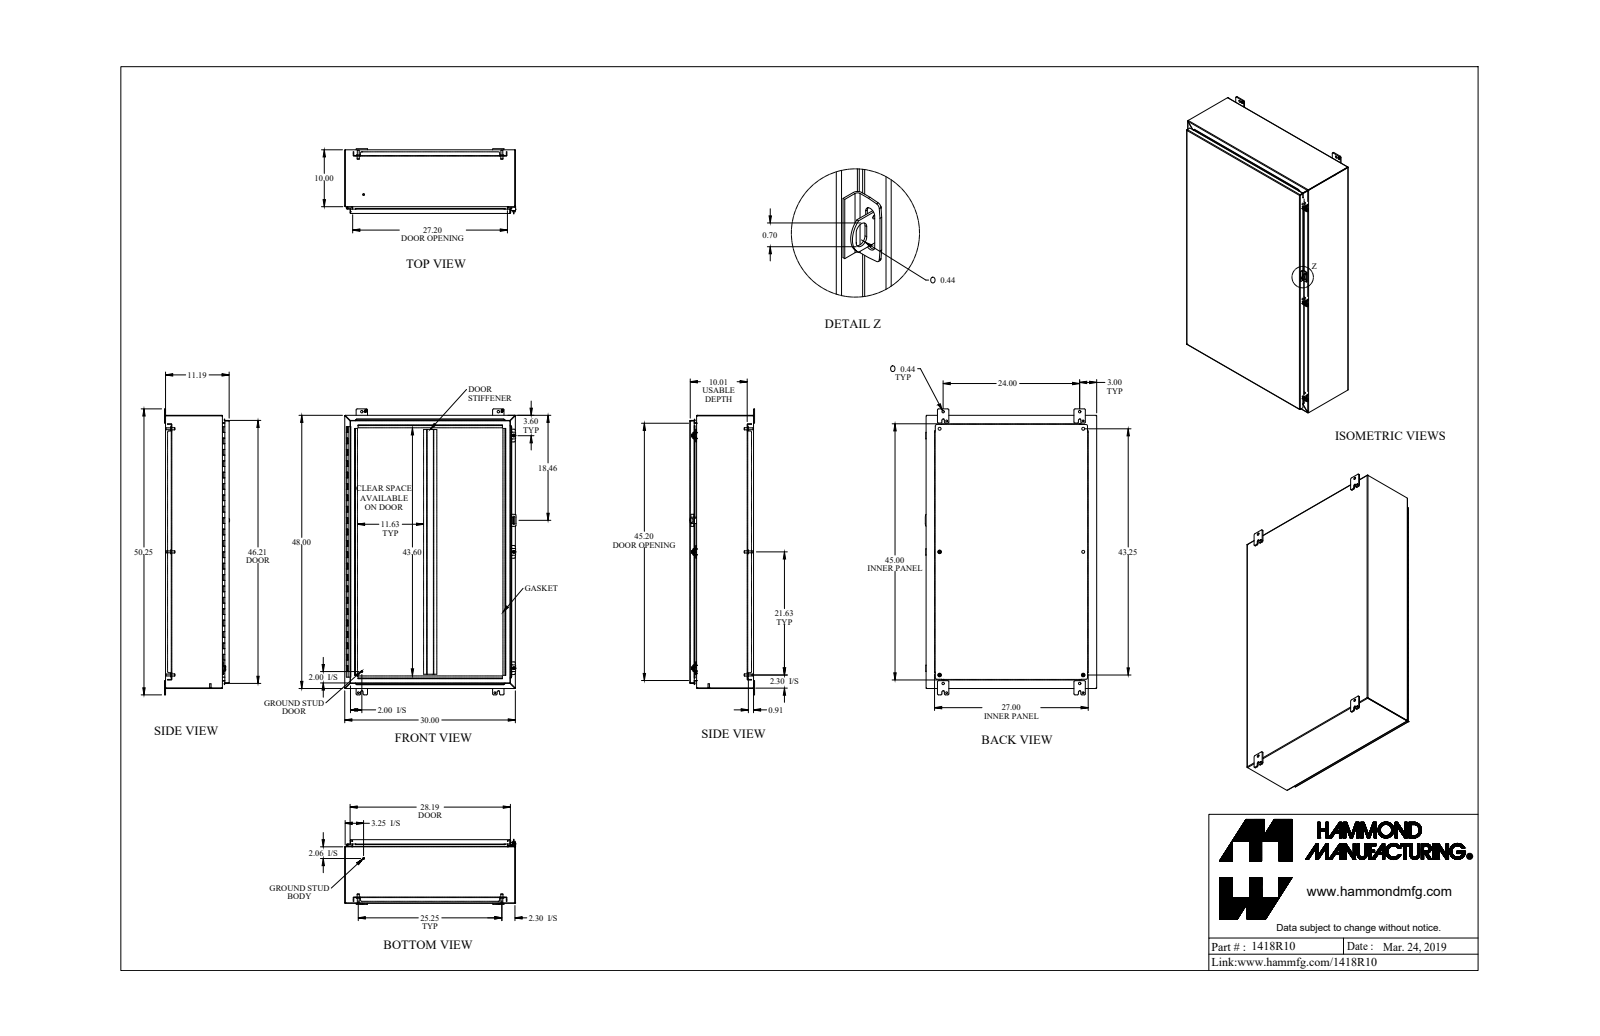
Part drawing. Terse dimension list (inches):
name: 1418R10_Default
written by: SolidWorks 2019 (CONFIG_CONTROL_DESIGN)
unit: in
bodies: 52 solids, 1711 faces (995 planar, 622 cylindrical, 94 other)
size: 50.25 × 30.125 × 11.437
volume: 529.6 in³; area: 13 753 in²
holes: 6× ⌀0.5, 4× ⌀0.307, 4× ⌀0.313, 4× ⌀0.437, 4× ⌀0.445, 3× ⌀0.213, 3× ⌀0.265, 3× ⌀0.375, 1× ⌀0.125, 1× ⌀0.187
bosses: 6× ⌀0.65, 6× ⌀0.375, 6× ⌀0.33, 4× ⌀1, 3× ⌀0.5, 3× ⌀0.39, 3× ⌀0.244, 2× ⌀0.281
rounds: 40× R0.188, 24× R0.036, 24× R0.108, 24× R0.25, 19× R0.048, 19× R0.143, 16× R0.116, 8× R0.04
face distances: 0.072, 11.113, 11.041, 11.185, 0.937, 0.095, 1.009, 10.081, 10.009, 1.032
hole spacings: 25.25, 21.625, 21.625, 24, 27.401, 33.244, 33.245, 43.25
